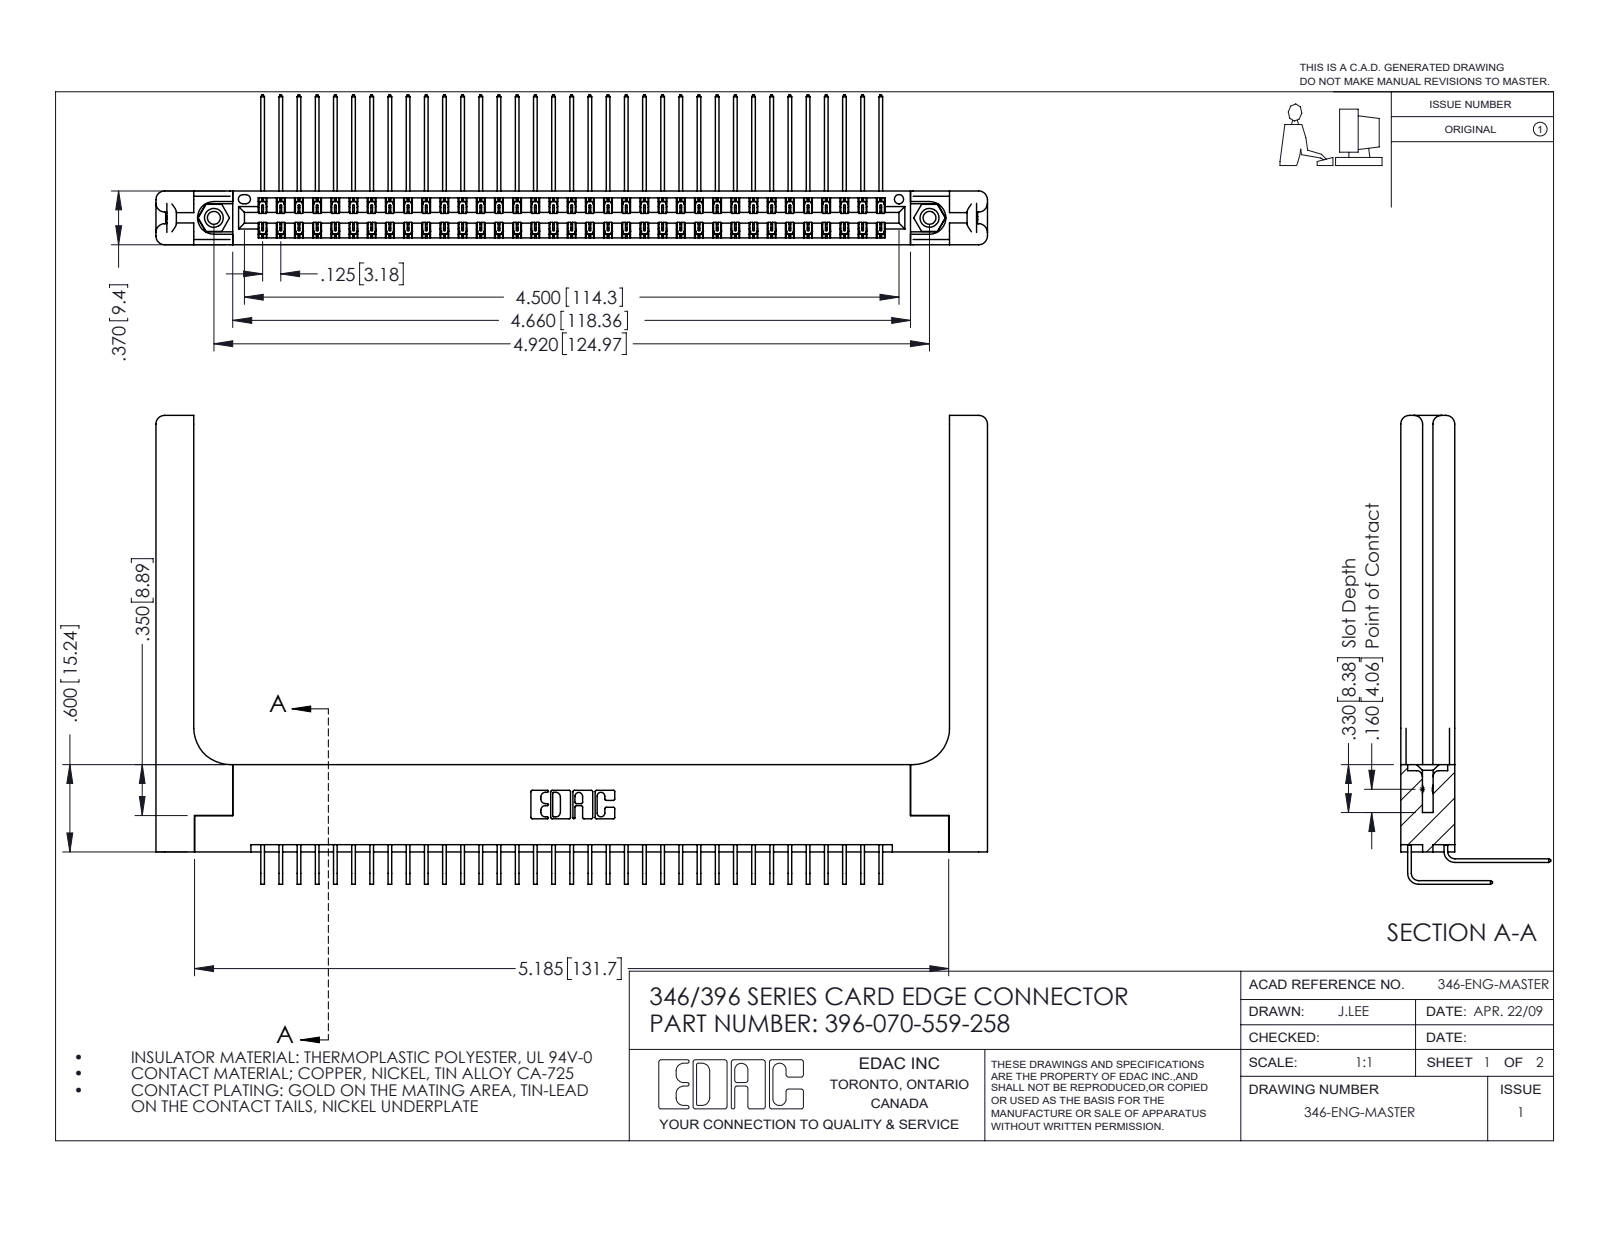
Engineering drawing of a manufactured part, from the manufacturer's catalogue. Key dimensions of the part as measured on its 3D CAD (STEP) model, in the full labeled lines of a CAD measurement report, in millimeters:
Part name (STEP PRODUCT): 345-292-001_559 Tail - 2; 396-070-559-258; 346-220-058_345-220-058; 346 Part_Flush Mounting Lugs - 0.156 Dia-TH (+2 more)
STEP written by: SolidWorks 2016 (CONFIG_CONTROL_DESIGN)
Units: millimetres
Bodies: 75 solids, 4158 faces (2814 planar, 1284 cylindrical, 60 other)
Overall size (bounding box): 145.2 × 81.9 × 26.2
Volume: 22 010 mm³ · Surface area: 26 740 mm²
Round holes (diameter × count): ⌀2.3 ×2, ⌀3.2 ×2, ⌀4 ×2, ⌀1.6 ×1
Round bosses / shafts (diameter × count): ⌀3.9 ×2
Partial cylindrical surfaces — rounded edges, fillets, slot ends (radius × count): R0.2 ×105, R0.3 ×22, R1.5 ×16, R0.2 ×6, R0.8 ×6, R0.7 ×3, R0.4 ×2, R0.6 ×2
Main face-to-face distances: 1.2, 9.4, 8.2, 1.8, 0.6, 3.8, 3.8, 6.4, 7.6, 7
Hole centre spacings: 6.2, 119.7, 125
